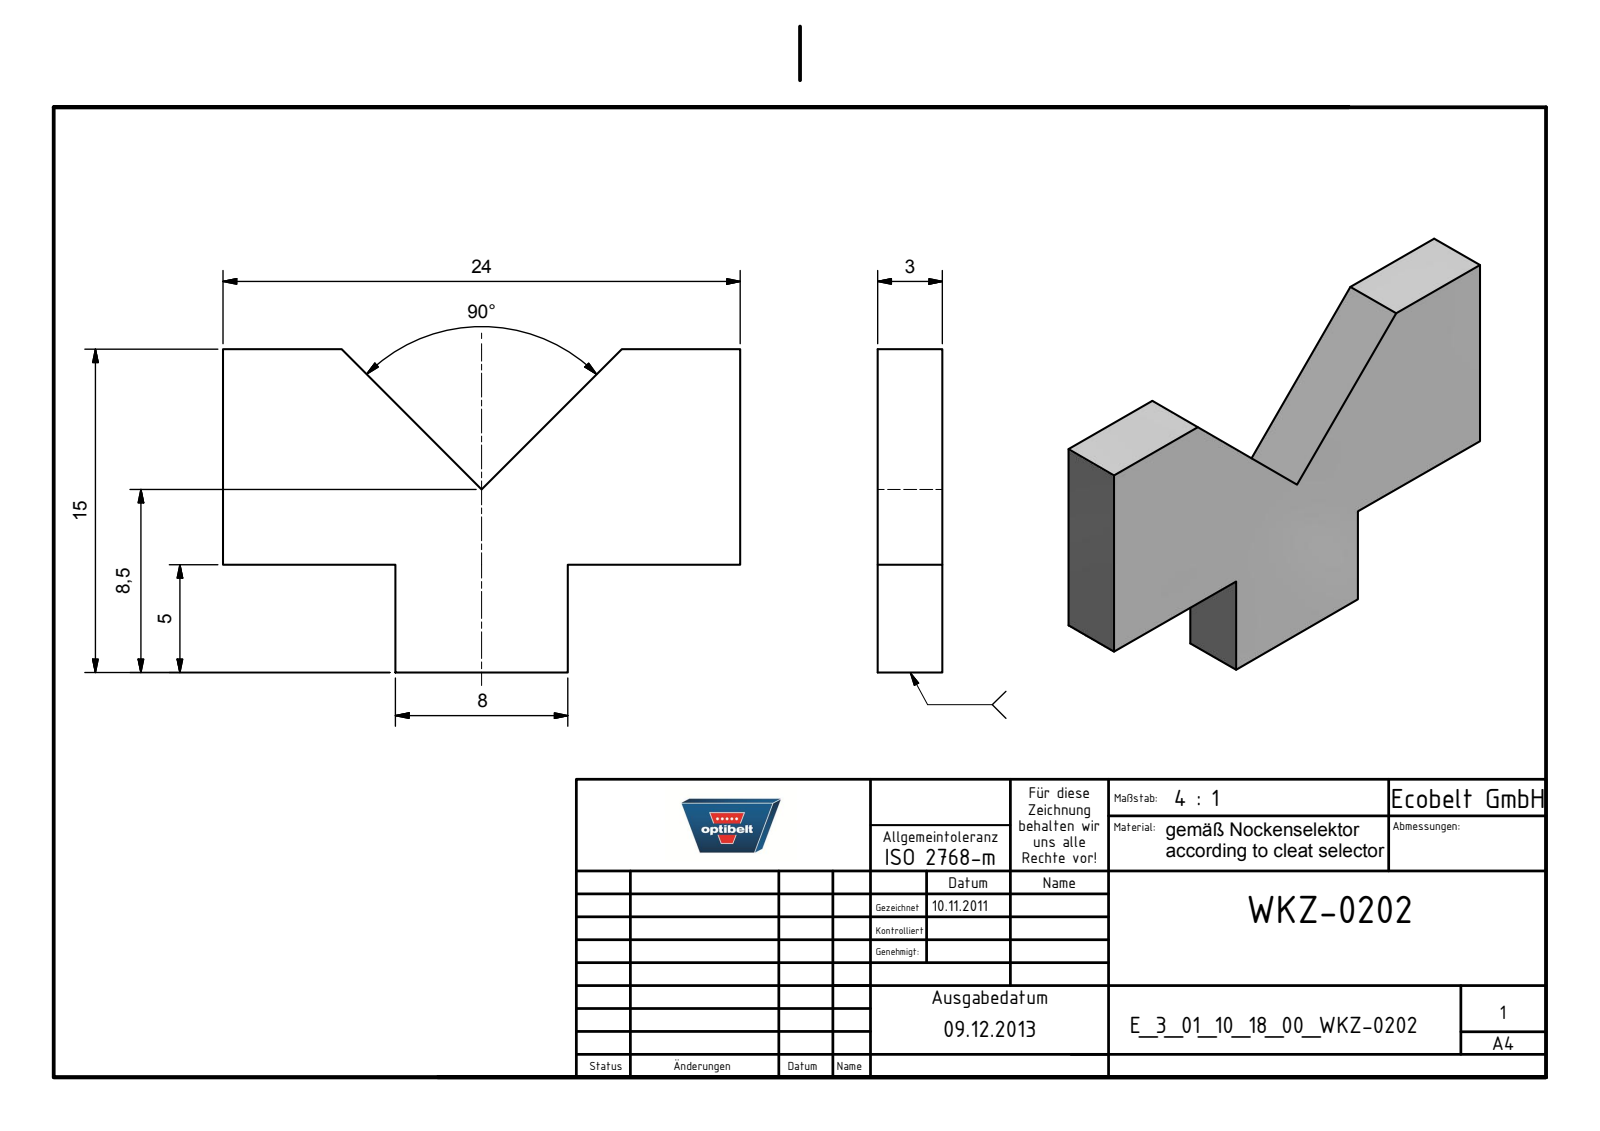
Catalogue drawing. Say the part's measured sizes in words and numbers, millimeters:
The part is named "E_3_01_10_18_00_WKZ-0202". Its 3-D file was written by "Autodesk Inventor 2025 (AUTOMOTIVE_DESIGN)". It is 1 solid with 13 faces: 13 planar, 0 cylindrical and 0 other. Overall it measures 24 by 15 by 3 millimeters. Its volume is 713 cubic millimeters and its surface area 726 square millimeters. The main face-to-face distances are 3, 8, 10, 24, 16, 5, 15.
